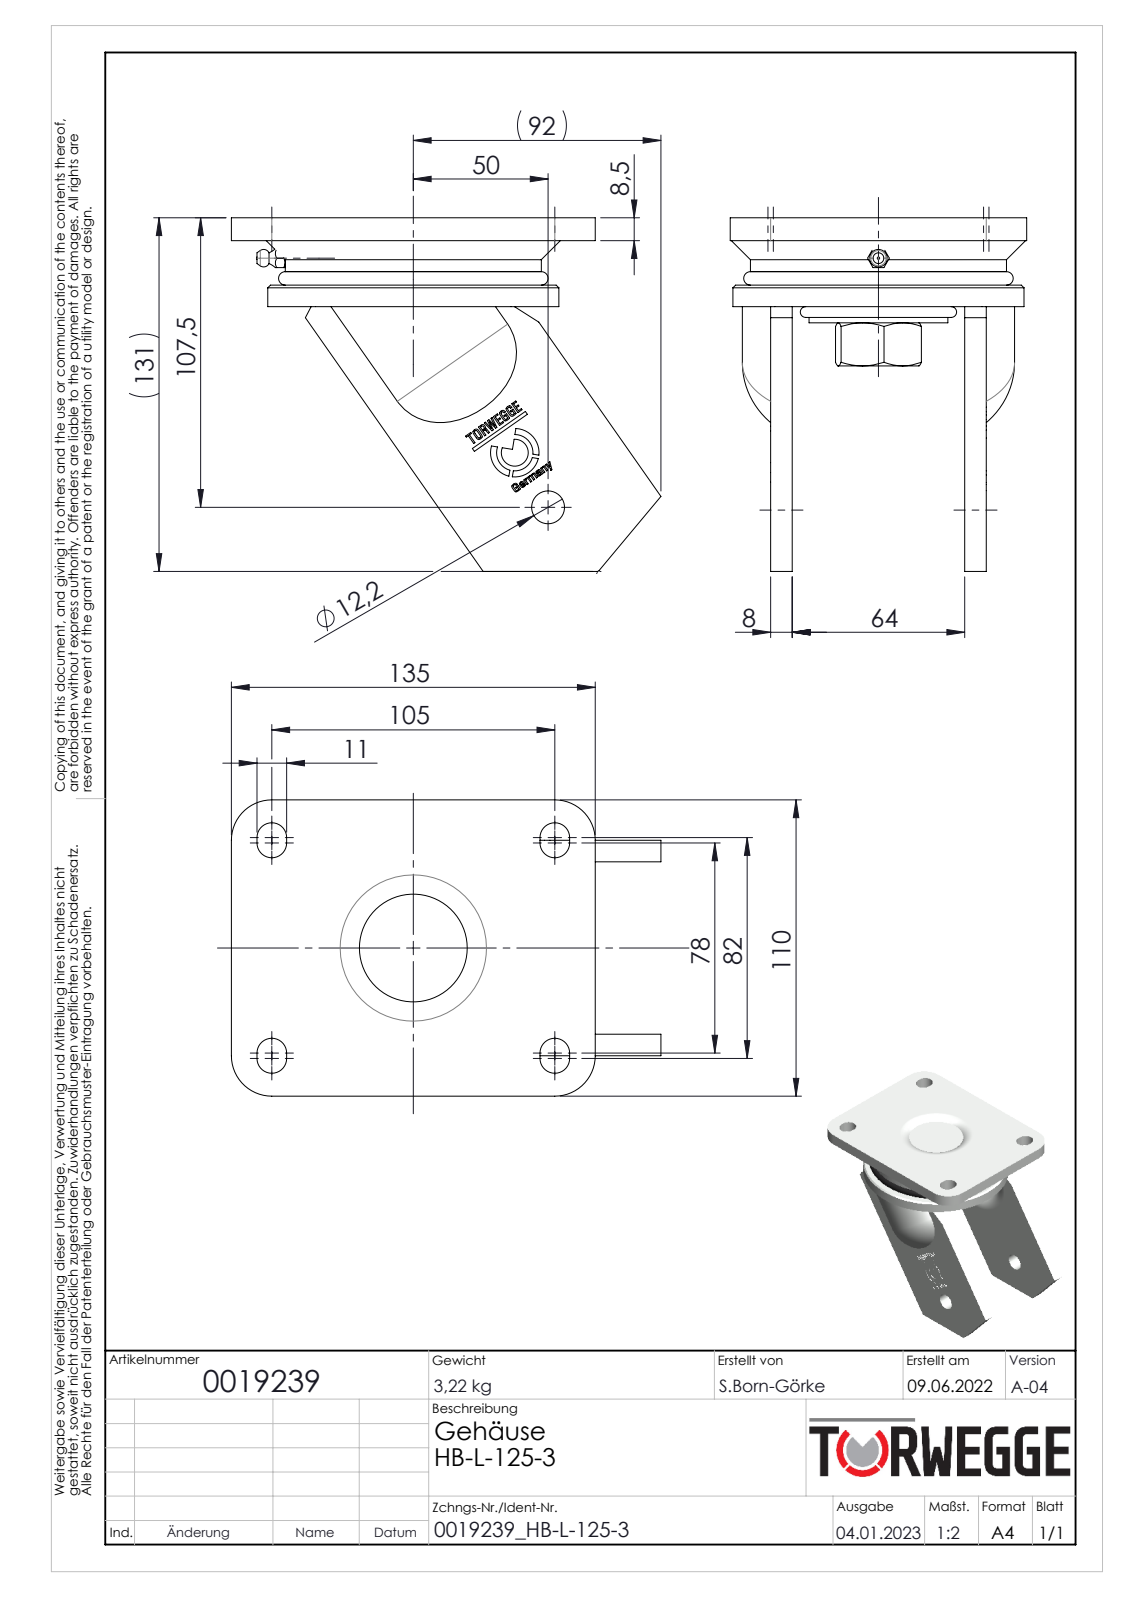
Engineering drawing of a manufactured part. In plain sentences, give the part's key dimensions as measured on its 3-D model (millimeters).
The part is named "0019239". Its 3-D file was written by "SolidWorks 2020 (AUTOMOTIVE_DESIGN)". It is 8 solids with 658 faces: 331 planar, 66 cylindrical and 261 other. Overall it measures 159.37 by 131.3 by 110 millimeters. Its volume is 451 964 cubic millimeters and its surface area 118 292 square millimeters. Round holes: 1 of diameter 6, 1 of diameter 10, 1 of diameter 12.2, 1 of diameter 17.29, 1 of diameter 20, 1 of diameter 25, 1 of diameter 95. Round bosses or shafts: 1 of diameter 108, 1 of diameter 51.5, 1 of diameter 19.79. Partial cylindrical surfaces (rounded edges, fillets, slot ends): 8 of radius 5.5, 4 of radius 10, 4 of radius 15, 2 of radius 27.01, 2 of radius 35.01, 1 of radius 1, 1 of radius 6.75, 1 of radius 9. The main face-to-face distances are 8, 72, 8.5, 16.5, 25, 23, 2, 24.5, 33, 10. The hole center spacings are 23.74.
